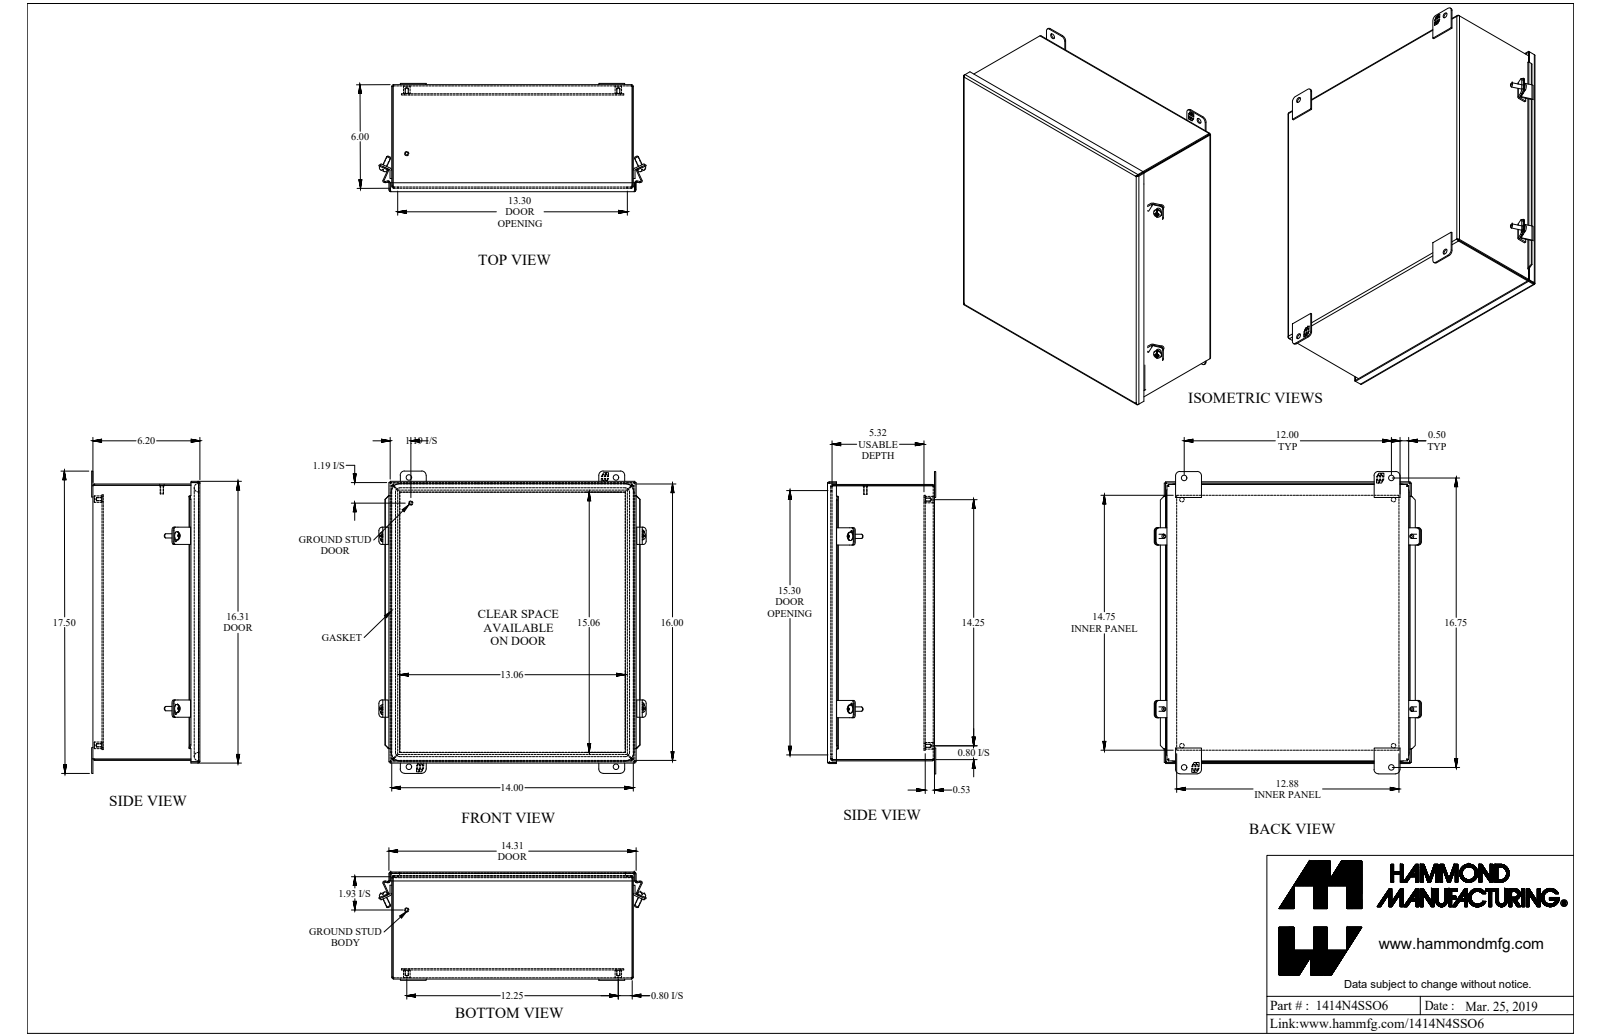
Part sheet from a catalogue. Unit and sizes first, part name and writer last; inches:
Units: inches
Overall size (bounding box): 17.5 × 15.475 × 6.269
Round holes (diameter × count): ⌀0.156 ×4, ⌀0.213 ×4, ⌀0.265 ×4, ⌀0.313 ×4
Round bosses / shafts (diameter × count): ⌀0.25 ×6, ⌀0.48 ×4, ⌀0.375 ×4, ⌀0.19 ×2
Partial cylindrical surfaces — rounded edges, fillets, slot ends (radius × count): R0.25 ×24, R0.188 ×16, R0.036 ×10, R0.108 ×10, R0.141 ×8, R0.007 ×4, R0.01 ×4, R0.029 ×4
Main face-to-face distances: 0.072, 6.125, 5.593, 0.532, 6.197, 6.053, 0.604, 5.665, 0.46, 5.521
Hole centre spacings: 12.189, 15.5, 19.679, 1.256, 12.25, 12.25, 14.25, 14.25
Volume: 82.72 in³ · Surface area: 2 292 in²
Bodies: 26 solids, 717 faces (473 planar, 168 cylindrical, 76 other)
Part name (STEP PRODUCT): 1414N4SSO6
STEP written by: SolidWorks 2018 (AUTOMOTIVE_DESIGN)
